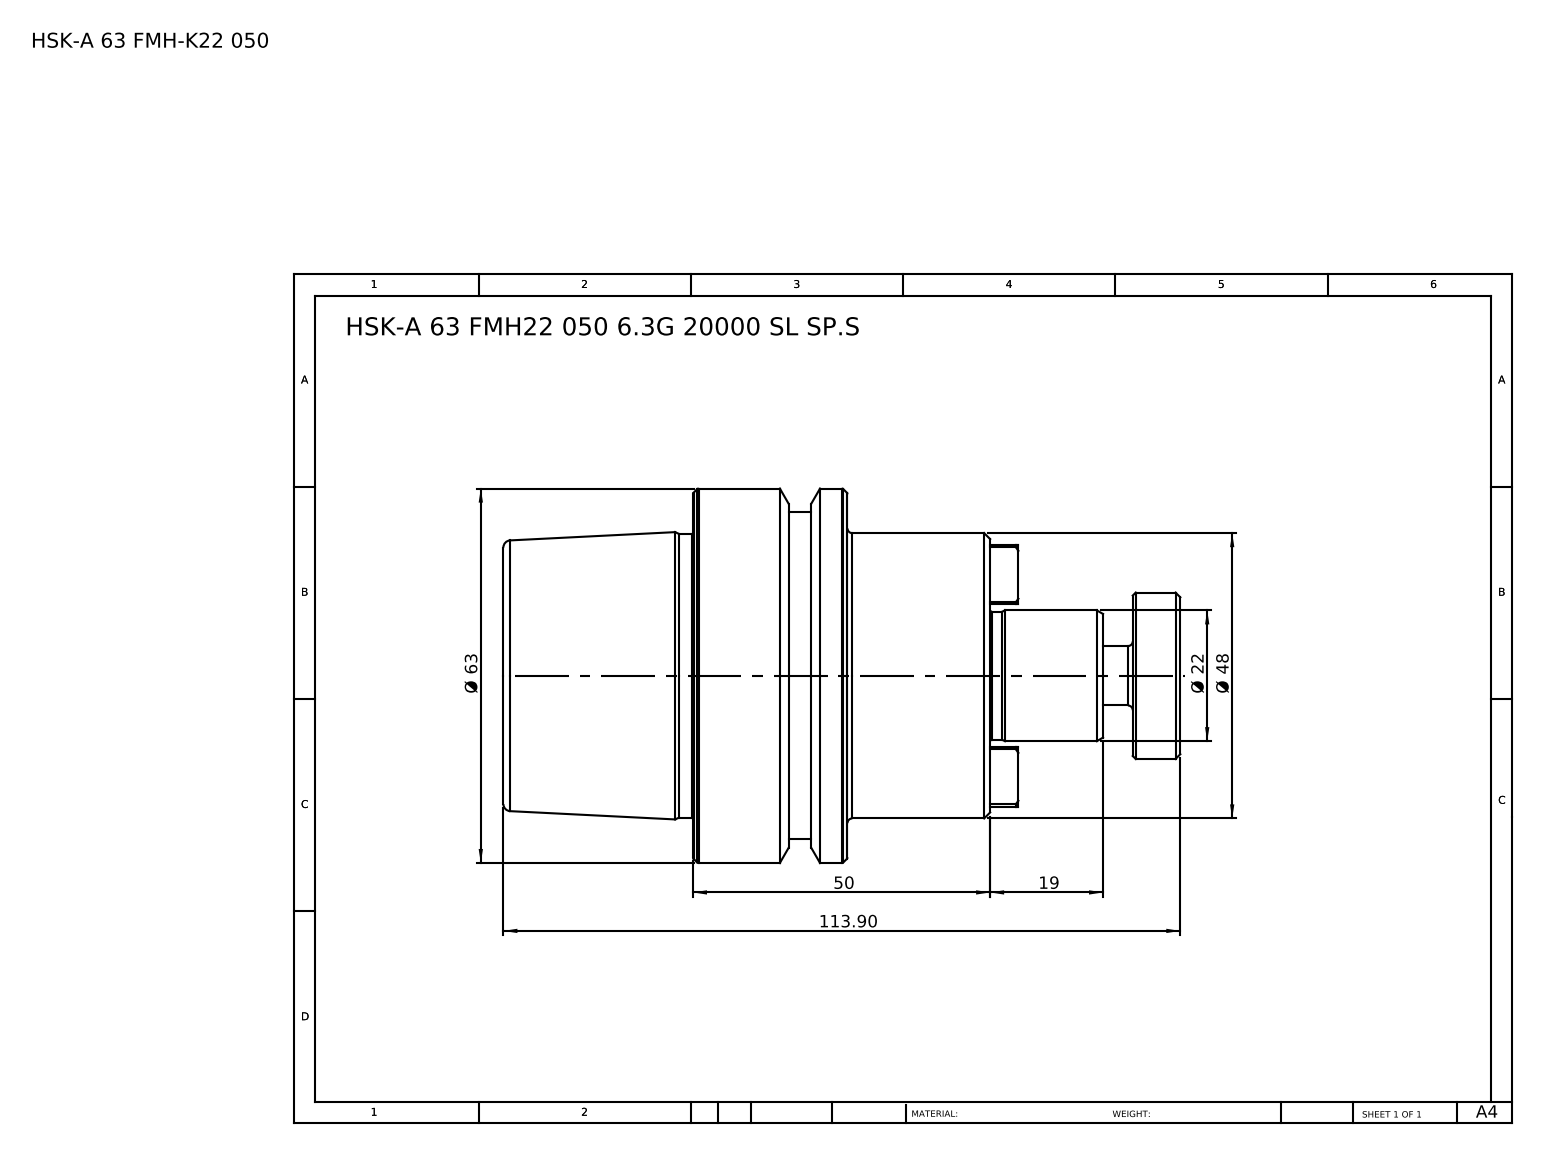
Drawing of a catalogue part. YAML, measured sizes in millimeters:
part_name: "HSK-A 63 FMH22 050 6.3G 20000 SL SP.S"
step_written_by: "SolidWorks 2014 (CONFIG_CONTROL_DESIGN)"
units: millimeters
bodies: {solids: 1, faces: 99, planar: 37, cylindrical: 18, other: 44}
overall_size: [113.9, 63, 63]
volume: 189336
surface_area: 23655
round_bosses_or_shafts:
  - {diameter: 63, count: 1}
  - {diameter: 55, count: 1}
  - {diameter: 48, count: 1}
  - {diameter: 47.78, count: 1}
  - {diameter: 28, count: 1}
  - {diameter: 22, count: 1}
  - {diameter: 21.6, count: 1}
  - {diameter: 10, count: 1}
face_to_face_distances: [24, 57.9, 81.9, 48, 50, 26, 31.9, 32, 56, 82]
